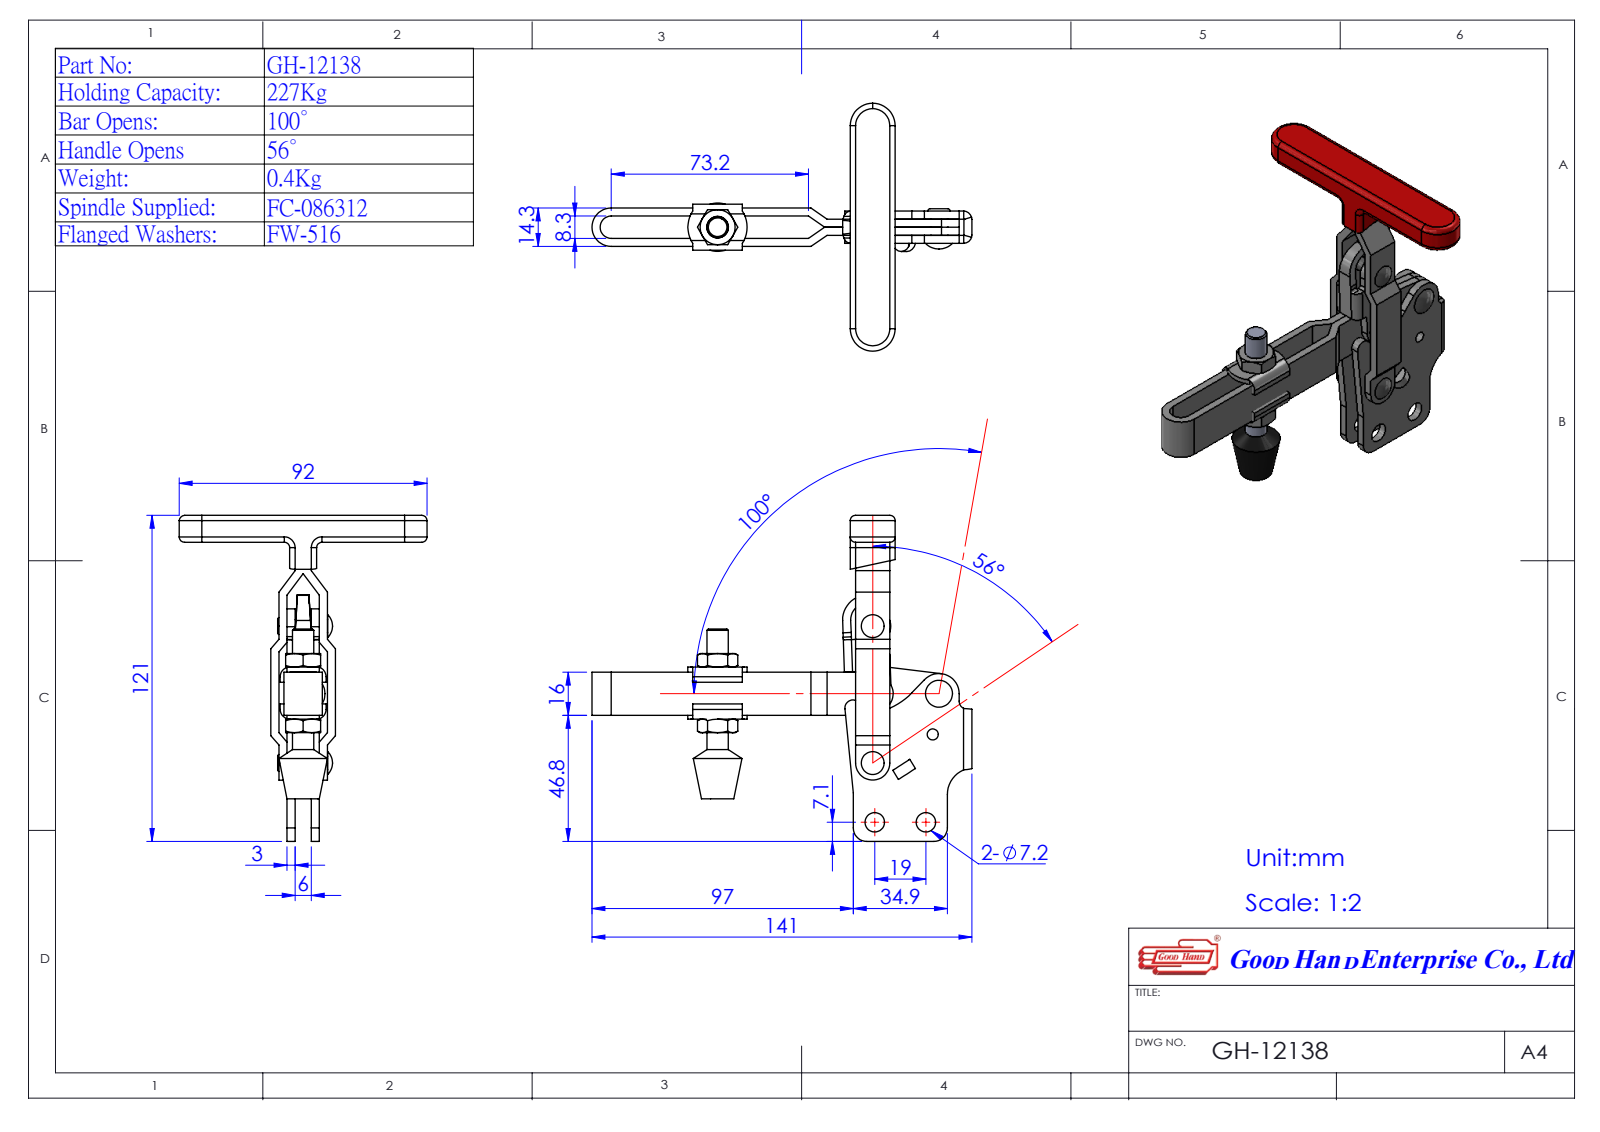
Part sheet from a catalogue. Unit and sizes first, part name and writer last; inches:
Units: inches
Overall size (bounding box): 5.551 × 4.764 × 3.622
Round holes (diameter × count): ⌀0.157 ×5, ⌀0.283 ×2
Round bosses / shafts (diameter × count): ⌀0.312 ×1, ⌀0.248 ×1
Partial cylindrical surfaces — rounded edges, fillets, slot ends (radius × count): R0.059 ×4, R0.295 ×4, R0.004 ×2, R0.039 ×2, R0.079 ×2, R0.118 ×2, R0.122 ×2, R0.252 ×2
Main face-to-face distances: 0.118, 0.354, 0.236, 0.472, 0.045, 0.4, 0.073, 0.518, 0.122, 0.114
Hole centre spacings: 0.601, 0.748, 0.867, 0.921, 0.972, 0.989, 1.013, 1.022
Volume: 3.737 in³ · Surface area: 58.74 in²
Bodies: 5 solids, 308 faces (154 planar, 98 cylindrical, 56 other)
Part name (STEP PRODUCT): Group2^GH-12138(簡化); Group4^GH-12138(簡化); Group5^GH-12138(簡化); Group1^EMC12141 (+2 more)
STEP written by: SolidWorks 2016 (AUTOMOTIVE_DESIGN)
